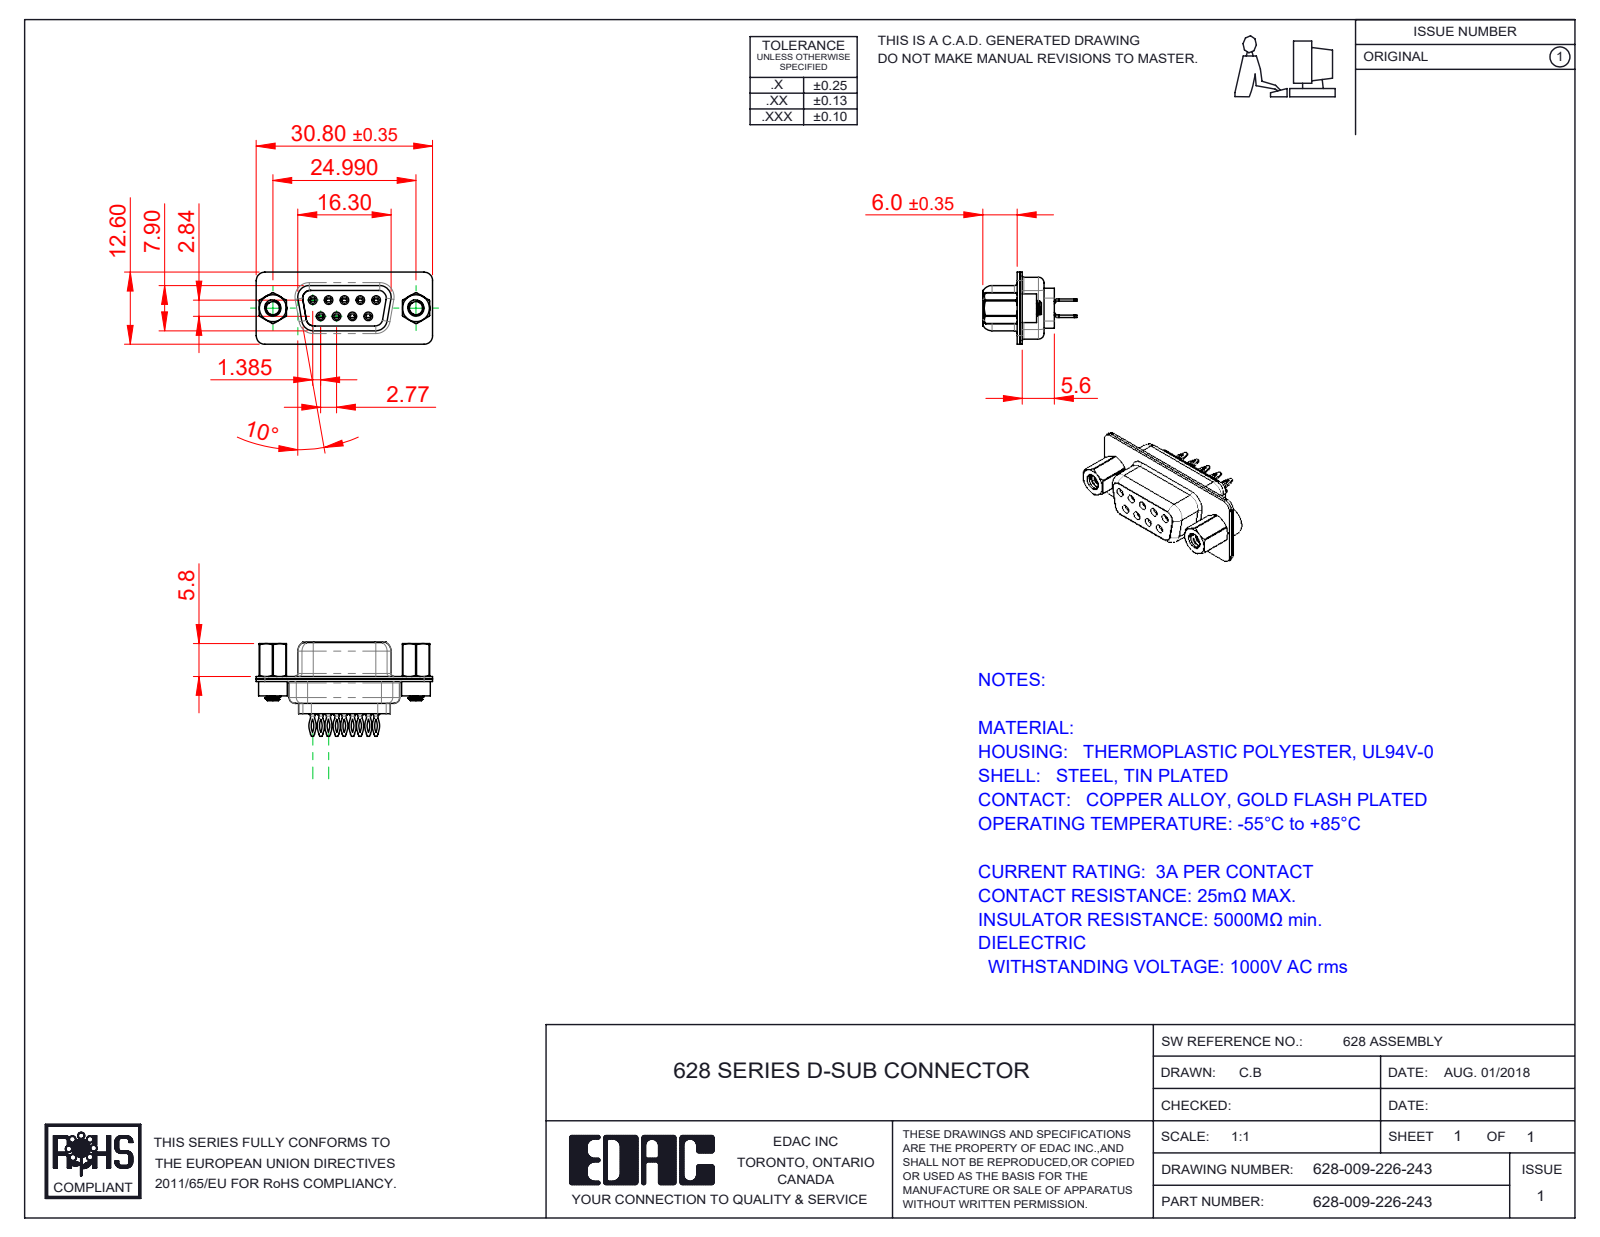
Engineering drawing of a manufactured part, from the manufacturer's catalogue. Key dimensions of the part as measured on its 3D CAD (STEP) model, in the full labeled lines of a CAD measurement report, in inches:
Part name (STEP PRODUCT): 628 Contact Row 1_26L; 628-009-226-243; 628 Contact Row 2_26L; 628 Housing_09 LP (+4 more)
STEP written by: SolidWorks 2020 (CONFIG_CONTROL_DESIGN)
Units: inches
Bodies: 16 solids, 1310 faces (332 planar, 450 cylindrical, 528 other)
Overall size (bounding box): 1.213 × 0.648 × 0.496
Volume: 0.12 in³ · Surface area: 7.673 in²
Round holes (diameter × count): ⌀0.031 ×9, ⌀0.035 ×9, ⌀0.043 ×9, ⌀0.063 ×9, ⌀0.067 ×5, ⌀0.089 ×2, ⌀0.09 ×2, ⌀0.157 ×2, ⌀0.159 ×2, ⌀0.191 ×2
Round bosses / shafts (diameter × count): ⌀0.079 ×9, ⌀0.059 ×9, ⌀0.047 ×9, ⌀0.197 ×2, ⌀0.195 ×2, ⌀0.189 ×2, ⌀0.11 ×2
Partial cylindrical surfaces — rounded edges, fillets, slot ends (radius × count): R0.115 ×18, R0.131 ×18, R0.059 ×17, R0.079 ×12, R0.011 ×9, R0.053 ×6, R0.01 ×4, R0.02 ×4
Main face-to-face distances: 0.018, 0.016, 0.035, 0.075, 0.335, 0.26, 0.055, 0.02, 0.492, 0.244
Hole centre spacings: 0.124, 0.109, 0.218, 0.198, 0.198, 0.327, 0.294, 0.295
